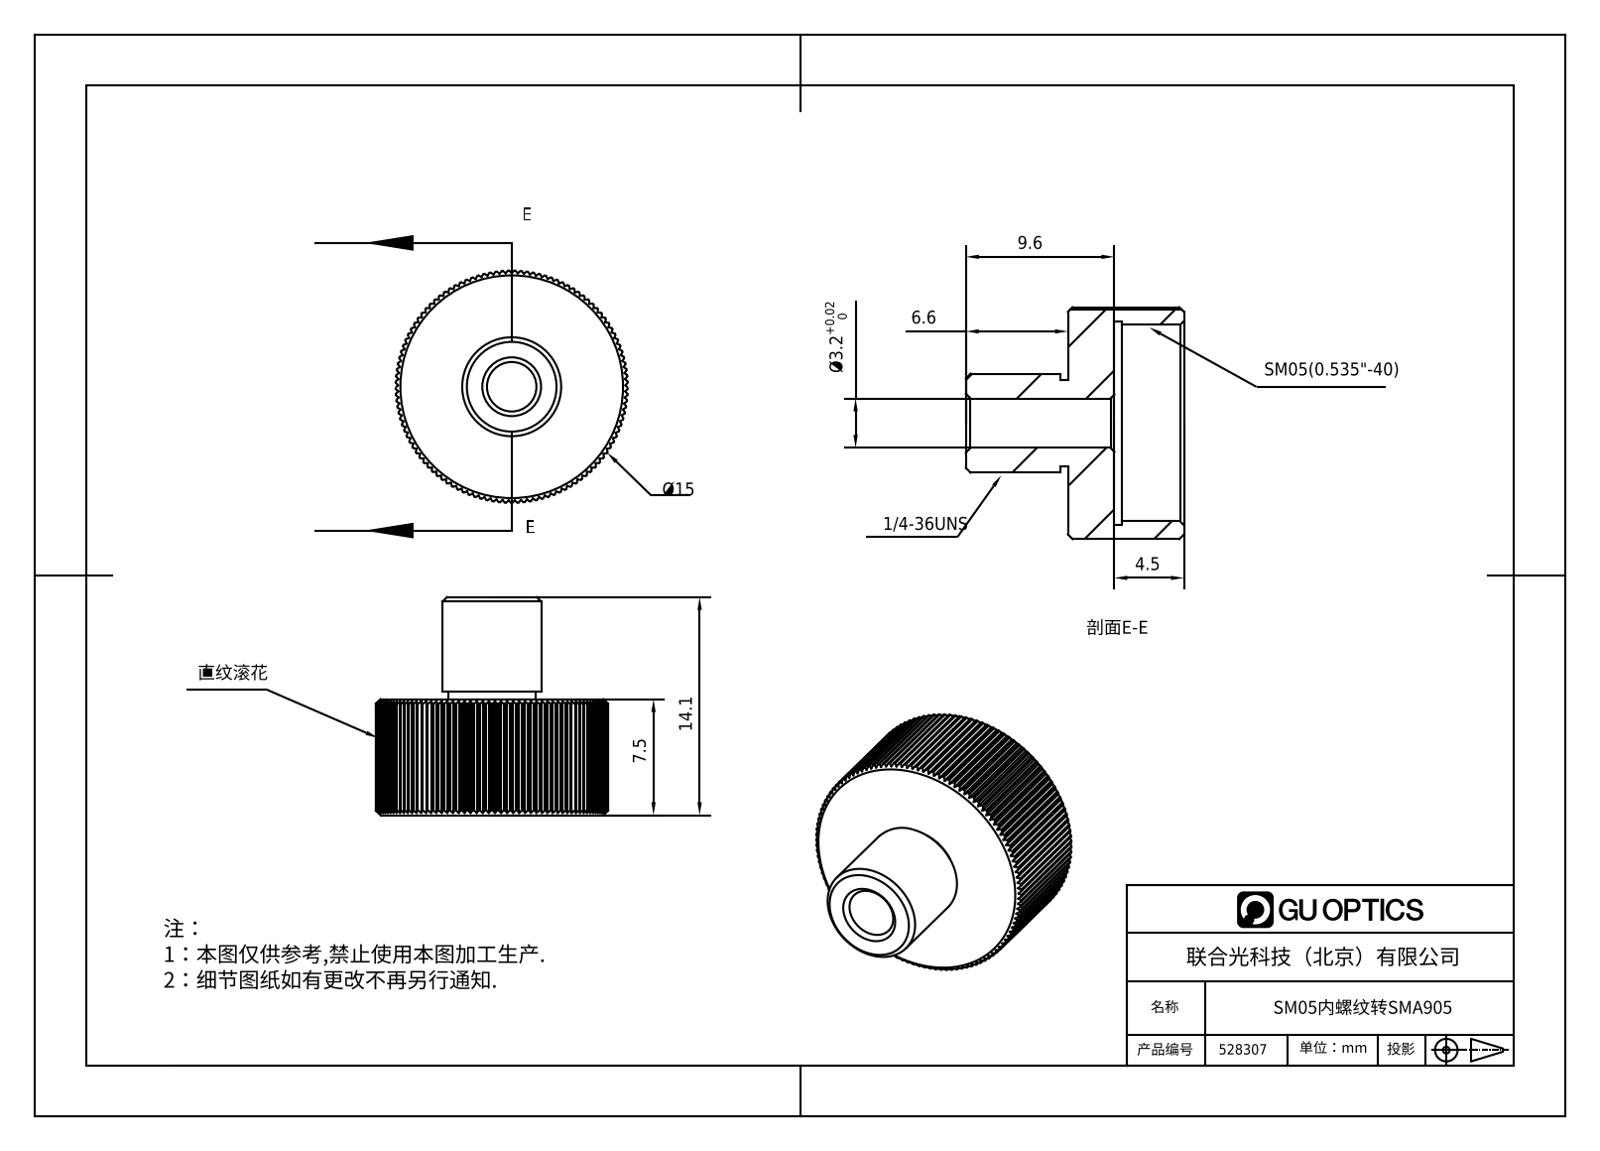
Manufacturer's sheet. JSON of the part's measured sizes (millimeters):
{"part_name": "528307", "step_written_by": "SolidWorks 2020 (CONFIG_CONTROL_DESIGN)", "units": "millimeters", "bodies": {"solids": 1, "faces": 379, "planar": 240, "cylindrical": 127, "other": 12}, "overall_size": [15, 15, 14.1], "volume_mm3": 856, "surface_area_mm2": 1205, "round_holes": [[3.2, 1], [12.7, 1], [13.2, 1]], "round_bosses_or_shafts": [[6.4, 1], [5.6, 1]], "partial_cylinders_radius": [[7.5, 1]], "face_to_face_distances": [3, 4.5, 7.5, 4, 0.5, 3.5, 14.1, 9.6, 6.6, 10.1]}
